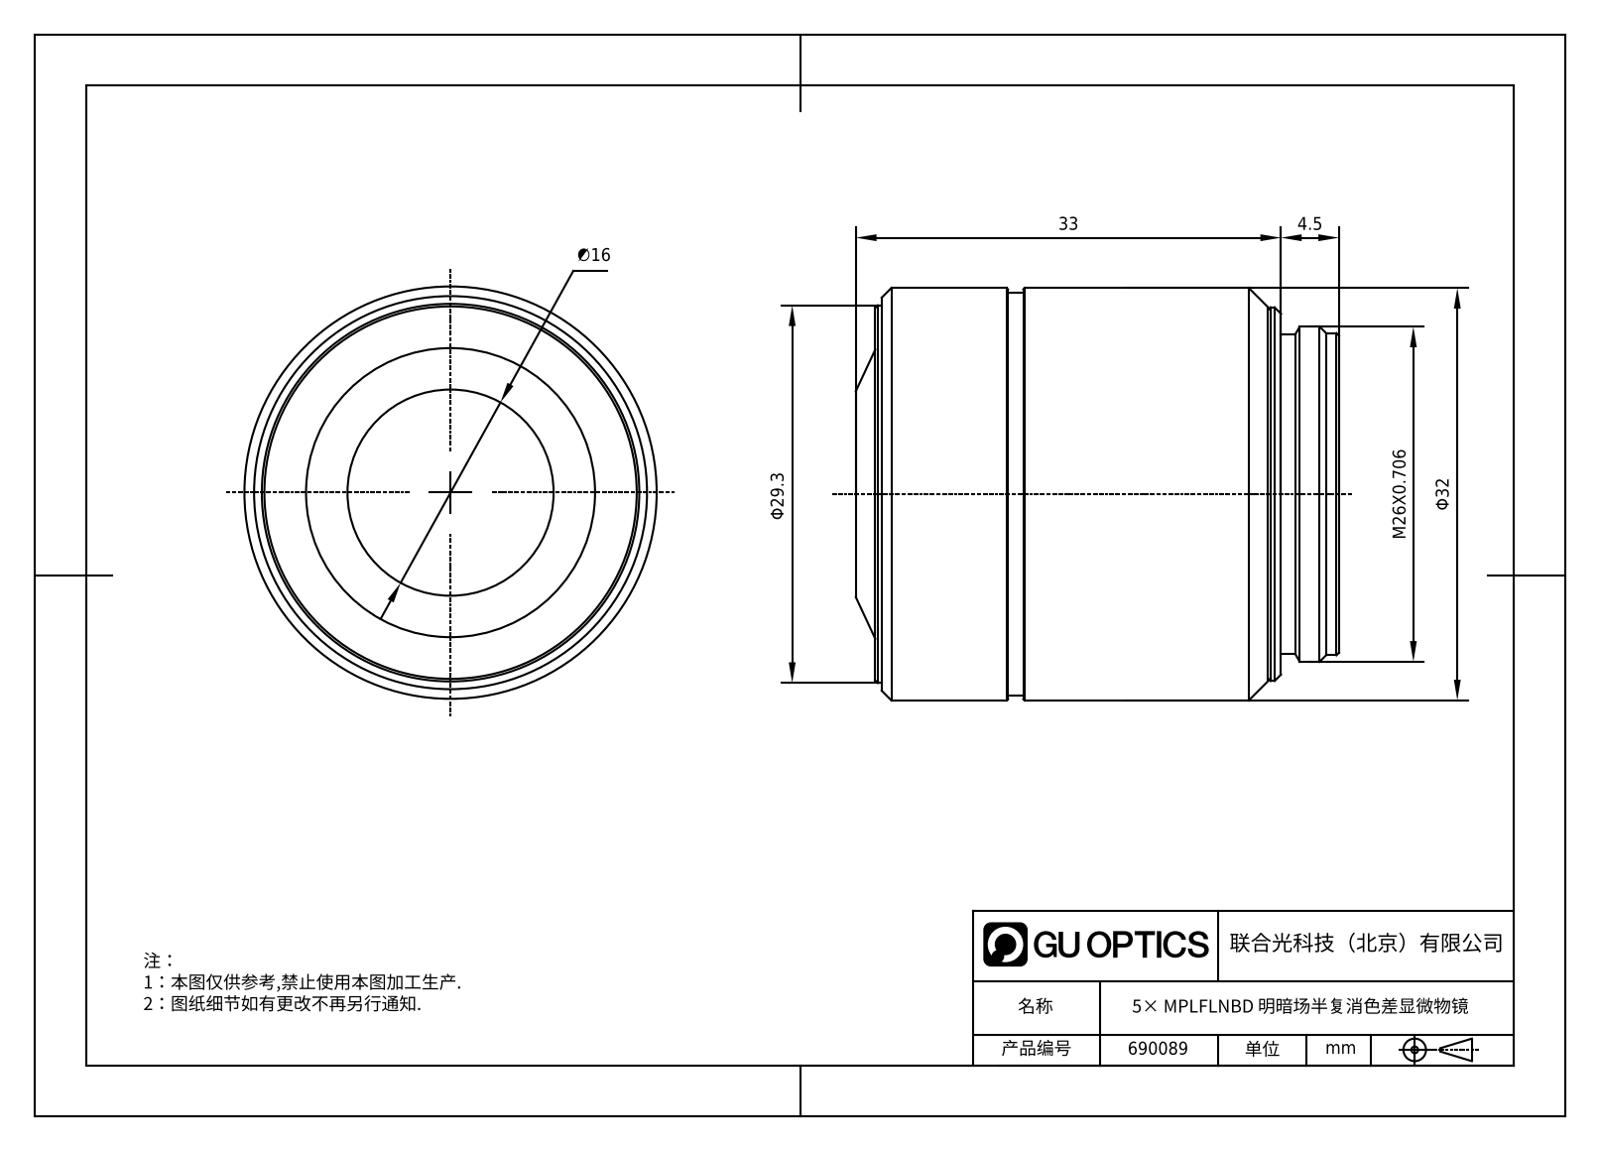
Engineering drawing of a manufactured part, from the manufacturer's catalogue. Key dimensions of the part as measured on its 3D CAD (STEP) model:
Part name (STEP PRODUCT): 690089; 690089.stp; MPLFLN5XBD.stp
STEP written by: SolidWorks 2020 (CONFIG_CONTROL_DESIGN)
Units: millimetres
Bodies: 1 solid, 46 faces (8 planar, 16 cylindrical, 22 other)
Overall size (bounding box): 37.5 × 32 × 32
Volume: 27 639 mm³ · Surface area: 5 100 mm²
Round bosses / shafts (diameter × count): ⌀32 ×1, ⌀31.2 ×1, ⌀29.3 ×1, ⌀29 ×1, ⌀26 ×1, ⌀25 ×1, ⌀24.78 ×1
Main face-to-face distances: 36, 1.5, 37.5, 33, 31.5, 4.5, 2, 0.5, 31, 35.5
